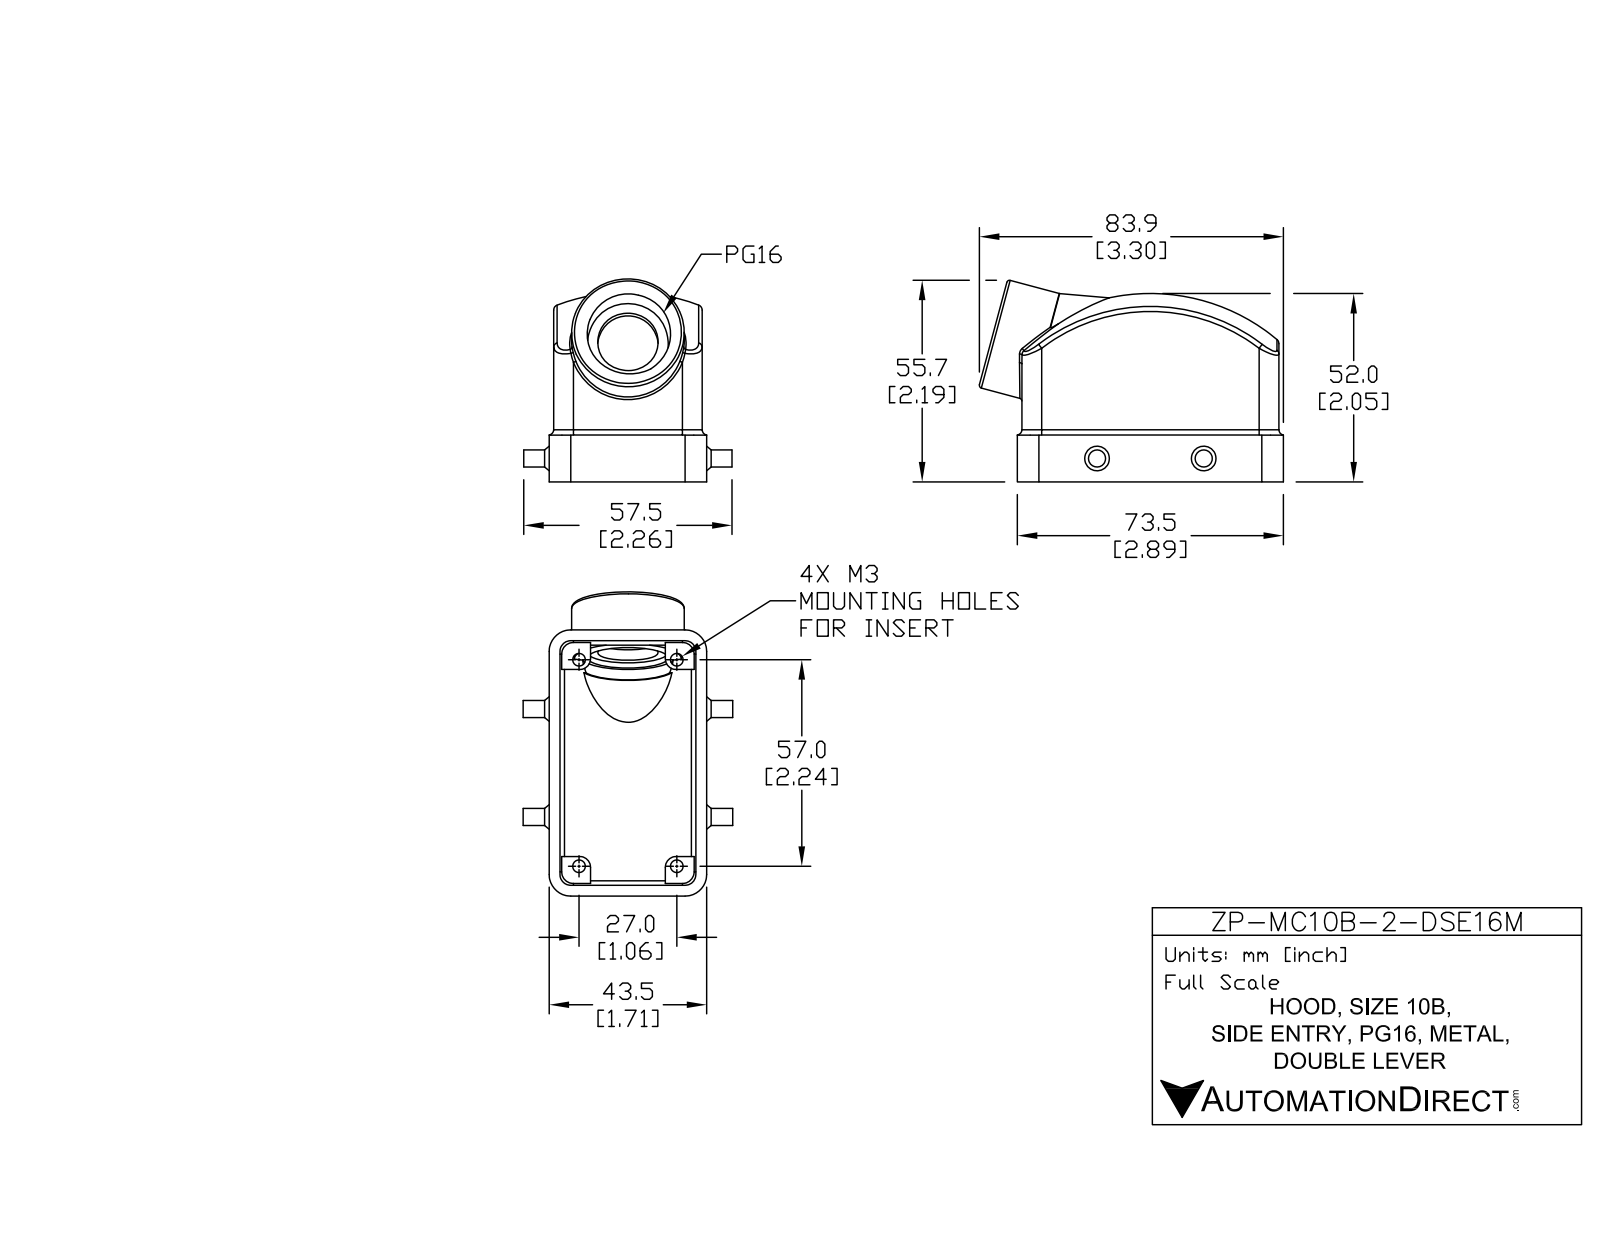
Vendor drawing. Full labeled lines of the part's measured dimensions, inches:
Part name (STEP PRODUCT): ZP-MC10B-2-DSE16M
STEP written by: SolidWorks 2011 (AUTOMOTIVE_DESIGN)
Units: inches
Bodies: 2 solids, 133 faces (46 planar, 47 cylindrical, 40 other)
Overall size (bounding box): 3.33 × 2.283 × 2.222
Volume: 2.632 in³ · Surface area: 44.76 in²
Round holes (diameter × count): ⌀0.138 ×4, ⌀0.65 ×1, ⌀0.866 ×1
Round bosses / shafts (diameter × count): ⌀0.187 ×2, ⌀1.22 ×1
Partial cylindrical surfaces — rounded edges, fillets, slot ends (radius × count): R0.118 ×8, R0.059 ×4, R0.177 ×4, R0.217 ×4, R0.236 ×4, R0.492 ×1, R0.581 ×1
Main face-to-face distances: 0.118, 0.049, 1.496, 1.545, 0.069, 0.167, 1.614, 1.378, 1.663, 1.594
Hole centre spacings: 1.043, 2.283, 2.511
